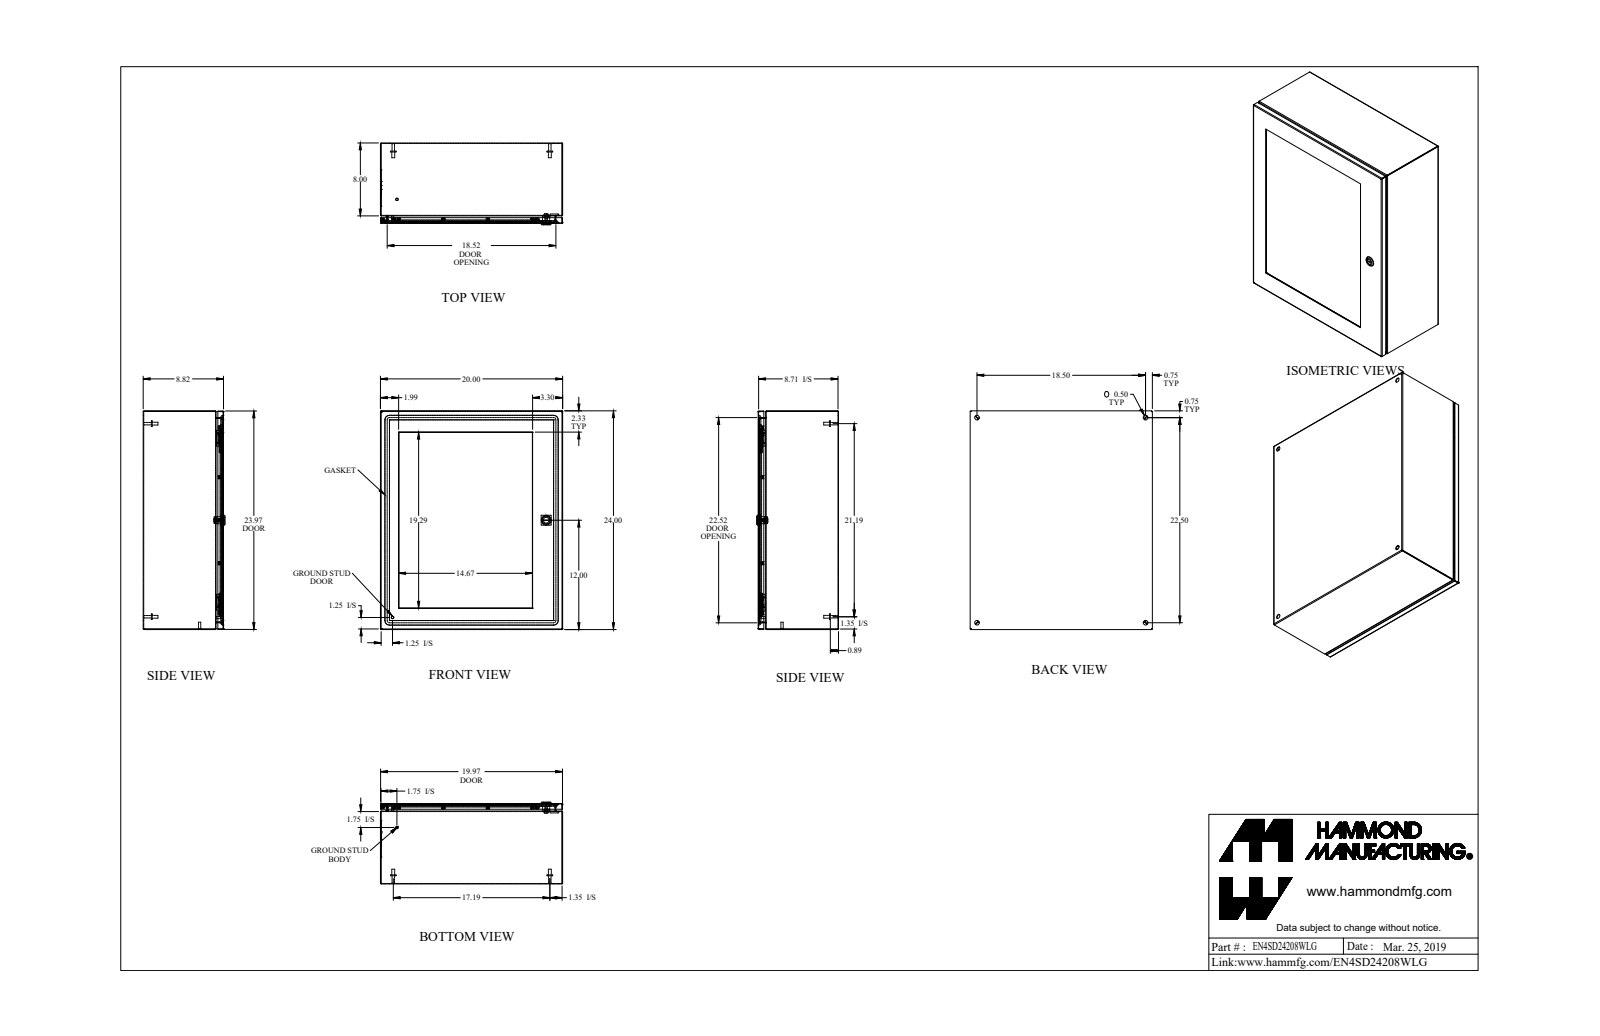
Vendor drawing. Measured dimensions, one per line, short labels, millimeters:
name: EN4SD24208WLG_Default
written by: SolidWorks 2019 (CONFIG_CONTROL_DESIGN)
unit: mm
bodies: 66 solids, 1333 faces (662 planar, 409 cylindrical, 262 other)
size: 609.6 × 508 × 228.1
volume: 2 932 000 mm³; area: 2 675 000 mm²
holes: 18× ⌀3.3, 18× ⌀6.4, 4× ⌀12.7, 1× ⌀4.4, 1× ⌀5.9, 1× ⌀6.1, 1× ⌀6.1, 1× ⌀15.9, 1× ⌀19.9
bosses: 19× ⌀5.7, 18× ⌀9.3, 18× ⌀4.2, 4× ⌀15.9, 4× ⌀8, 4× ⌀6.9, 2× ⌀7.1, 2× ⌀6.4
rounds: 21× R0.7, 21× R2.2, 16× R6.4, 10× R3.2, 8× R482.6, 4× R0.2, 4× R0.4, 4× R1.6
face distances: 1.4, 222.6, 221.2, 506.6, 6.4, 214.8, 216.3, 608.2, 505.1, 508
hole spacings: 119.9, 124.2, 124.2, 248.4, 262.2, 416.6, 465.4, 516.5
